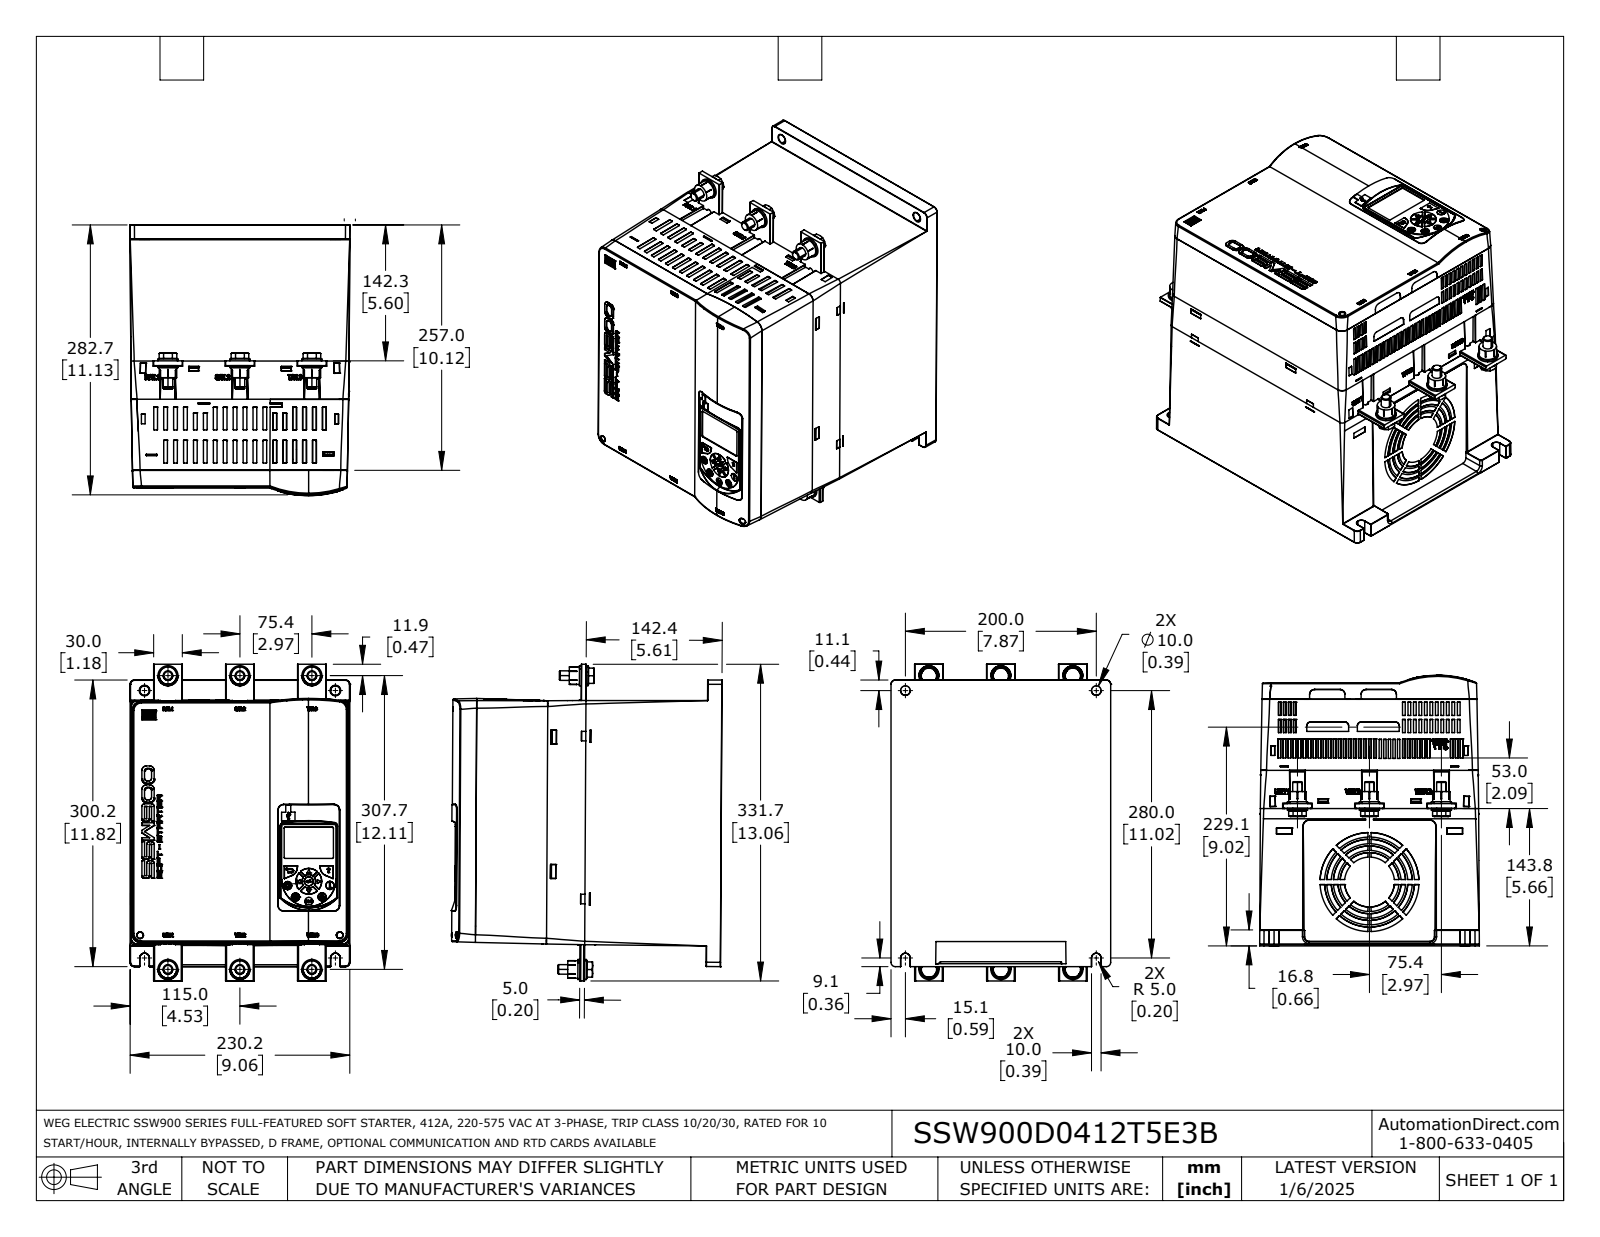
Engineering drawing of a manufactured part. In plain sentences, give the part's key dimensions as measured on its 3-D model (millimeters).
The part is named "SSW900D0412T5E3B". Its 3-D file was written by "SolidWorks 2021 (AUTOMOTIVE_DESIGN)". It is 1 solid with 4211 faces: 2804 planar, 500 cylindrical and 907 other. Overall it measures 331.7 by 283.5 by 230.1 millimeters. Its volume is 2 838 000 cubic millimeters and its surface area 813 500 square millimeters. Round holes: 2 of diameter 10, 1 of diameter 3.4, 1 of diameter 6.6, 1 of diameter 61.7, 1 of diameter 75.7, 1 of diameter 89.7, 1 of diameter 103.7. Round bosses or shafts: 9 of diameter 21, 6 of diameter 18.3, 6 of diameter 10, 1 of diameter 94.3, 1 of diameter 80.3, 1 of diameter 66.3, 1 of diameter 3.8, 1 of diameter 1.4. Partial cylindrical surfaces (rounded edges, fillets, slot ends): 103 of radius 0.3, 24 of radius 0.5, 22 of radius 0.4, 22 of radius 0.5, 20 of radius 0.5, 17 of radius 1, 7 of radius 0.2, 6 of radius 2. The main face-to-face distances are 17.9, 248.4, 274.2, 256.3, 2.5, 17.2, 257, 239.1, 14.8, 271.7. The hole center spacings are 200, 257.6, 328.9.
